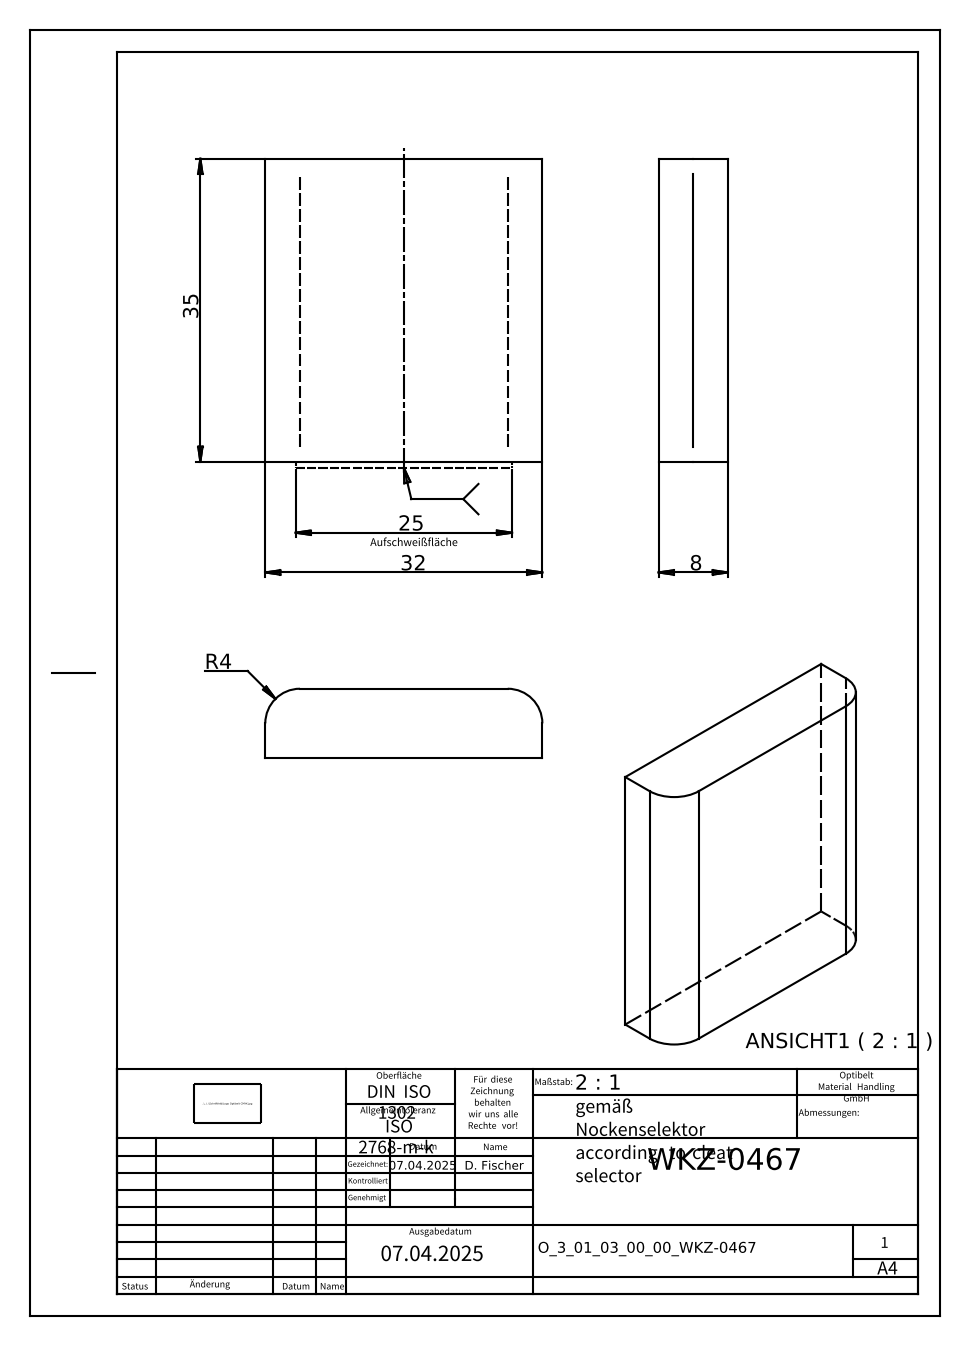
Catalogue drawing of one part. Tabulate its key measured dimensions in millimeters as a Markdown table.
| quantity | value |
| --- | --- |
| part name | O_3_01_03_00_00_WKZ-0467 |
| STEP written by | Autodesk Inventor 2025 (AUTOMOTIVE_DESIGN) |
| units | millimeters |
| bodies | 1 solid, 8 faces (6 planar, 2 cylindrical, 0 other) |
| overall size | 35 × 32 × 8 |
| volume | 8 720 mm³ |
| surface area | 3 178 mm² |
| partial cylindrical surfaces (radius × count) | 4 × 2 |
| main face-to-face distances | 8, 35, 32 |
